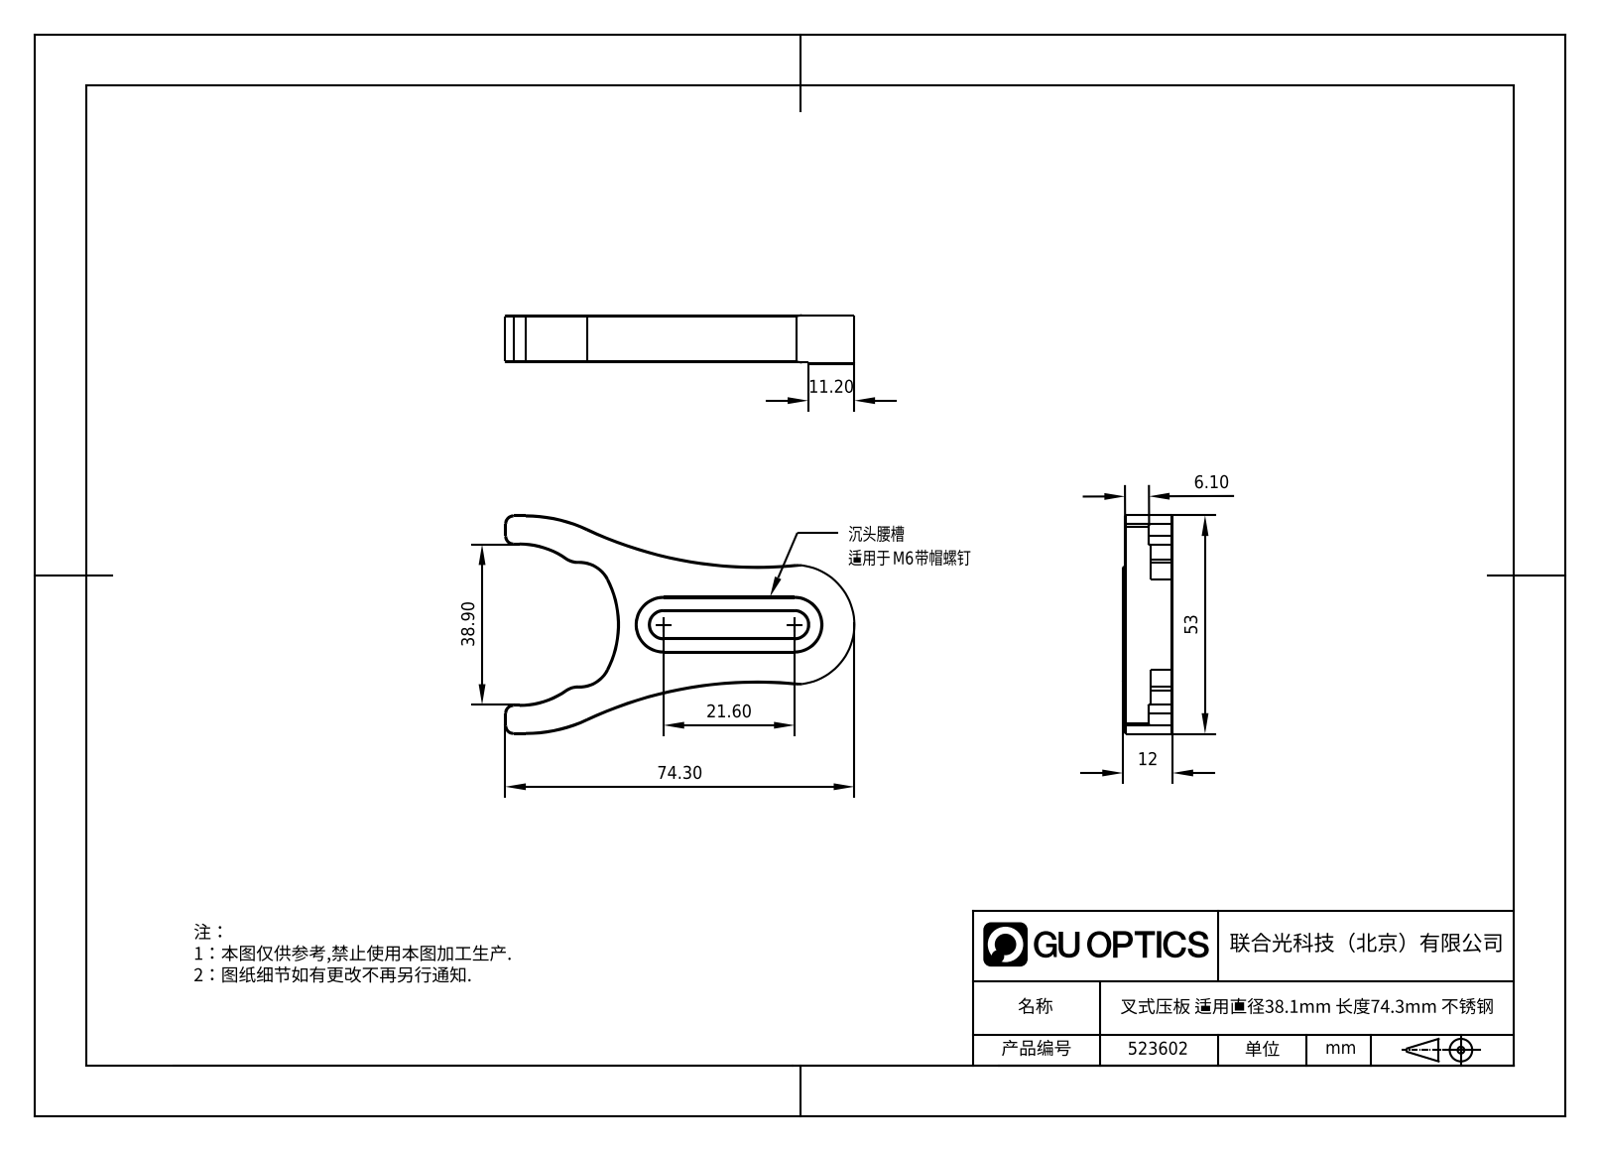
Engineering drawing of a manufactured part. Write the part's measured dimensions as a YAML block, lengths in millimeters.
part_name: "1.4.5.21_ZGY-1.5A_不锈钢1.5英寸光学叉型压板，A型"
step_written_by: "SolidWorks 2021 (CONFIG_CONTROL_DESIGN)"
units: millimeters
bodies: {solids: 1, faces: 111, planar: 44, cylindrical: 27, other: 40}
overall_size: [74.3, 53, 12]
volume: 16886
surface_area: 7096
partial_cylinders:
  - {radius: 2, count: 4}
  - {radius: 0.5, count: 2}
  - {radius: 3.3, count: 2}
  - {radius: 4, count: 2}
  - {radius: 5, count: 2}
  - {radius: 6.5, count: 2}
  - {radius: 7.5, count: 2}
  - {radius: 35, count: 2}
face_to_face_distances: [11.5, 0.5, 6.6, 5.3, 6.2, 5.8, 12, 3.2, 9.8, 6.1]
